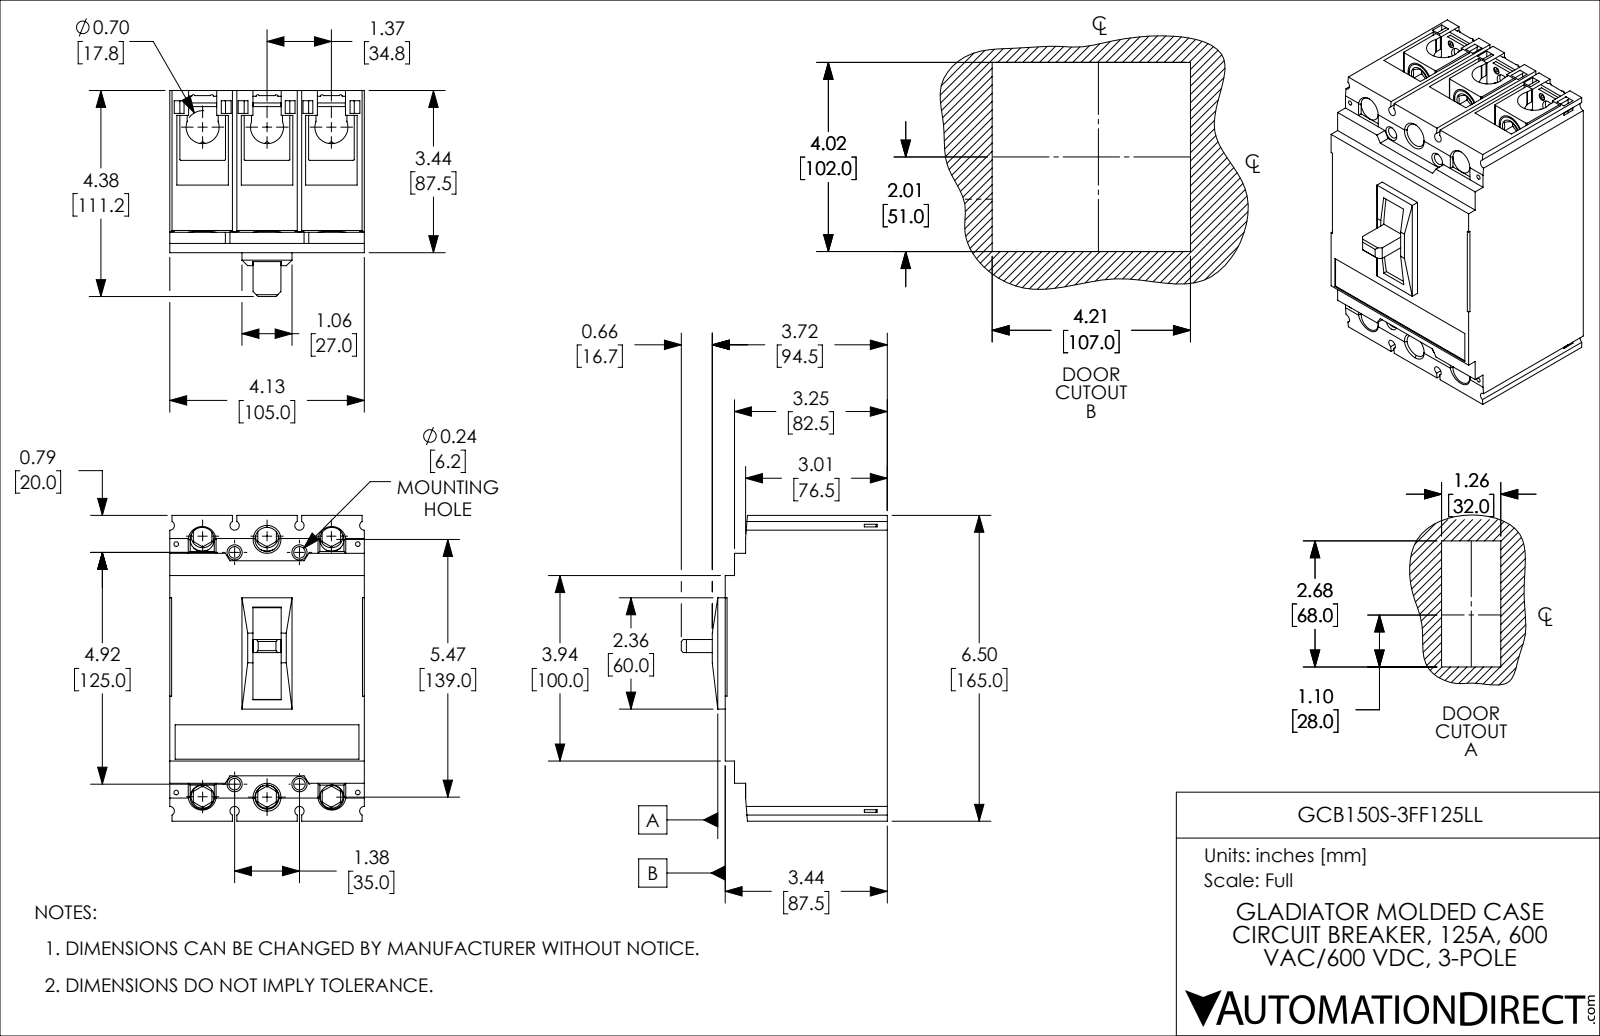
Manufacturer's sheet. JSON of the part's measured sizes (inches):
{"part_name": "GCB150S-3FF125LL", "step_written_by": "SolidWorks 2021 (CONFIG_CONTROL_DESIGN)", "units": "inches", "bodies": {"solids": 19, "faces": 1004, "planar": 544, "cylindrical": 381, "other": 79}, "overall_size": [6.496, 4.376, 4.134], "volume_in3": 80.08, "surface_area_in2": 248.1, "round_holes": [[0.067, 24], [0.157, 24], [0.098, 10], [0.354, 6], [0.512, 6], [0.689, 6], [0.197, 4], [0.244, 4]], "round_bosses_or_shafts": [[0.709, 6]], "partial_cylinders_radius": [[0.039, 36], [0.008, 24], [0.016, 6], [0.02, 6], [0.031, 6], [0.098, 4], [0.35, 3], [5.638, 1]], "face_to_face_distances": [1.368, 4.134, 0.063, 1.031, 0.846, 0.866, 3.445, 5.63, 2.736, 0.264], "hole_center_spacings": [1.378, 0.285, 1.368, 0.571, 0.742, 0.75, 5.242, 5.809]}
